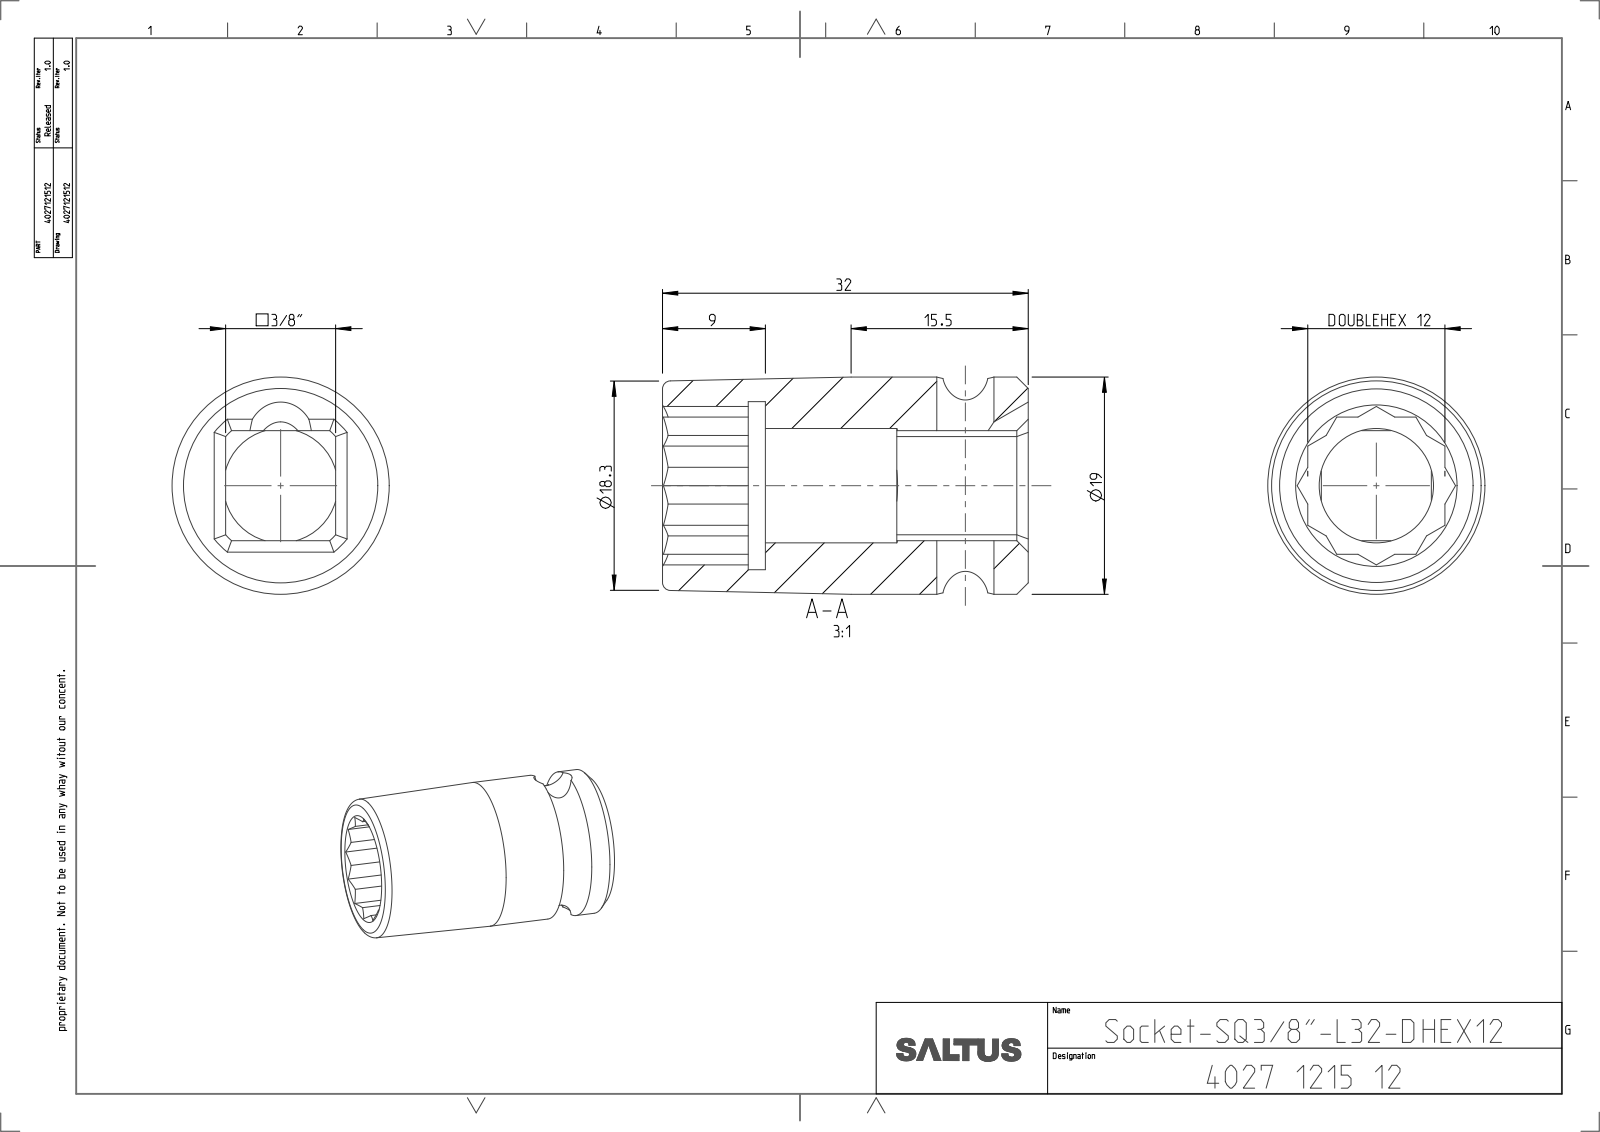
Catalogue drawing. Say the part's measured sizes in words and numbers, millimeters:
The part is named "4027121512". Its 3-D file was written by "CREO PARAMETRIC BY PTC INC, 2022414 (CONFIG_CONTROL_DESIGN)". It is 1 solid with 76 faces: 41 planar, 17 cylindrical and 18 other. Overall it measures 32 by 19 by 19 millimeters. Its volume is 5 212 cubic millimeters and its surface area 3 550 square millimeters. Round holes: 1 of diameter 5, 1 of diameter 10, 1 of diameter 14.7. Round bosses or shafts: 1 of diameter 19. Partial cylindrical surfaces (rounded edges, fillets, slot ends): 1 of radius 3, 1 of radius 6.45. The main face-to-face distances are 12, 9.62, 1.19, 10.81, 23, 32, 9, 24.5, 1.5, 7.5.
